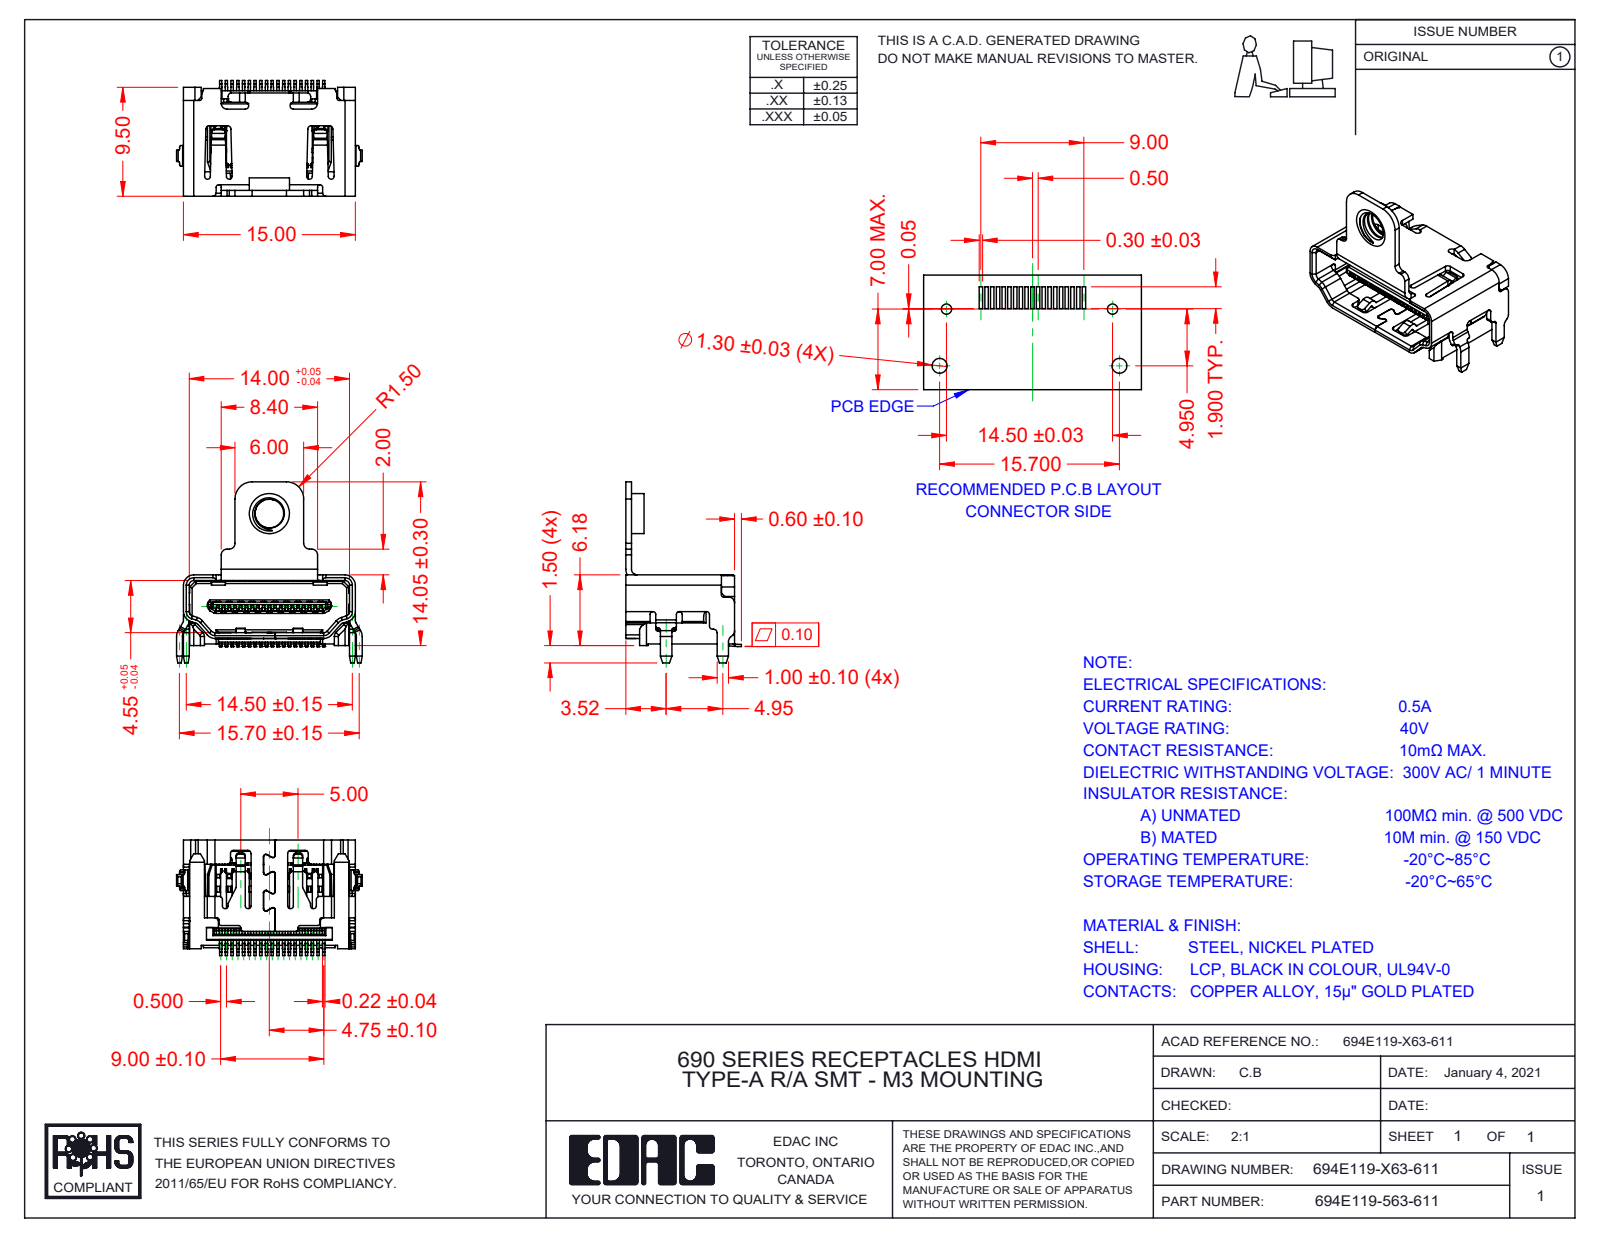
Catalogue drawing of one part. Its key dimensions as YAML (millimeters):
part_name: "694E119-163-611; Insulator 694E119-X63-611; Contact Lower 694E119-X63-611; Contact Upper 694E119-X63-611 (+1 more)"
step_written_by: "SolidWorks 2020 (AUTOMOTIVE_DESIGN)"
units: millimeters
bodies: {solids: 21, faces: 2892, planar: 1971, cylindrical: 793, other: 128}
overall_size: [16.2, 15.8, 10.1]
volume: 376
surface_area: 1571
round_holes:
  - {diameter: 2.5, count: 1}
round_bosses_or_shafts:
  - {diameter: 3.5, count: 1}
partial_cylinders:
  - {radius: 0.2, count: 35}
  - {radius: 0.3, count: 24}
  - {radius: 0.5, count: 22}
  - {radius: 0.25, count: 19}
  - {radius: 0.15, count: 18}
  - {radius: 1, count: 11}
  - {radius: 0.35, count: 8}
  - {radius: 0.4, count: 8}
face_to_face_distances: [0.5, 2.52, 0.49, 2.02, 3.02, 2.4, 14.5, 0.55, 2.53, 5.05]
